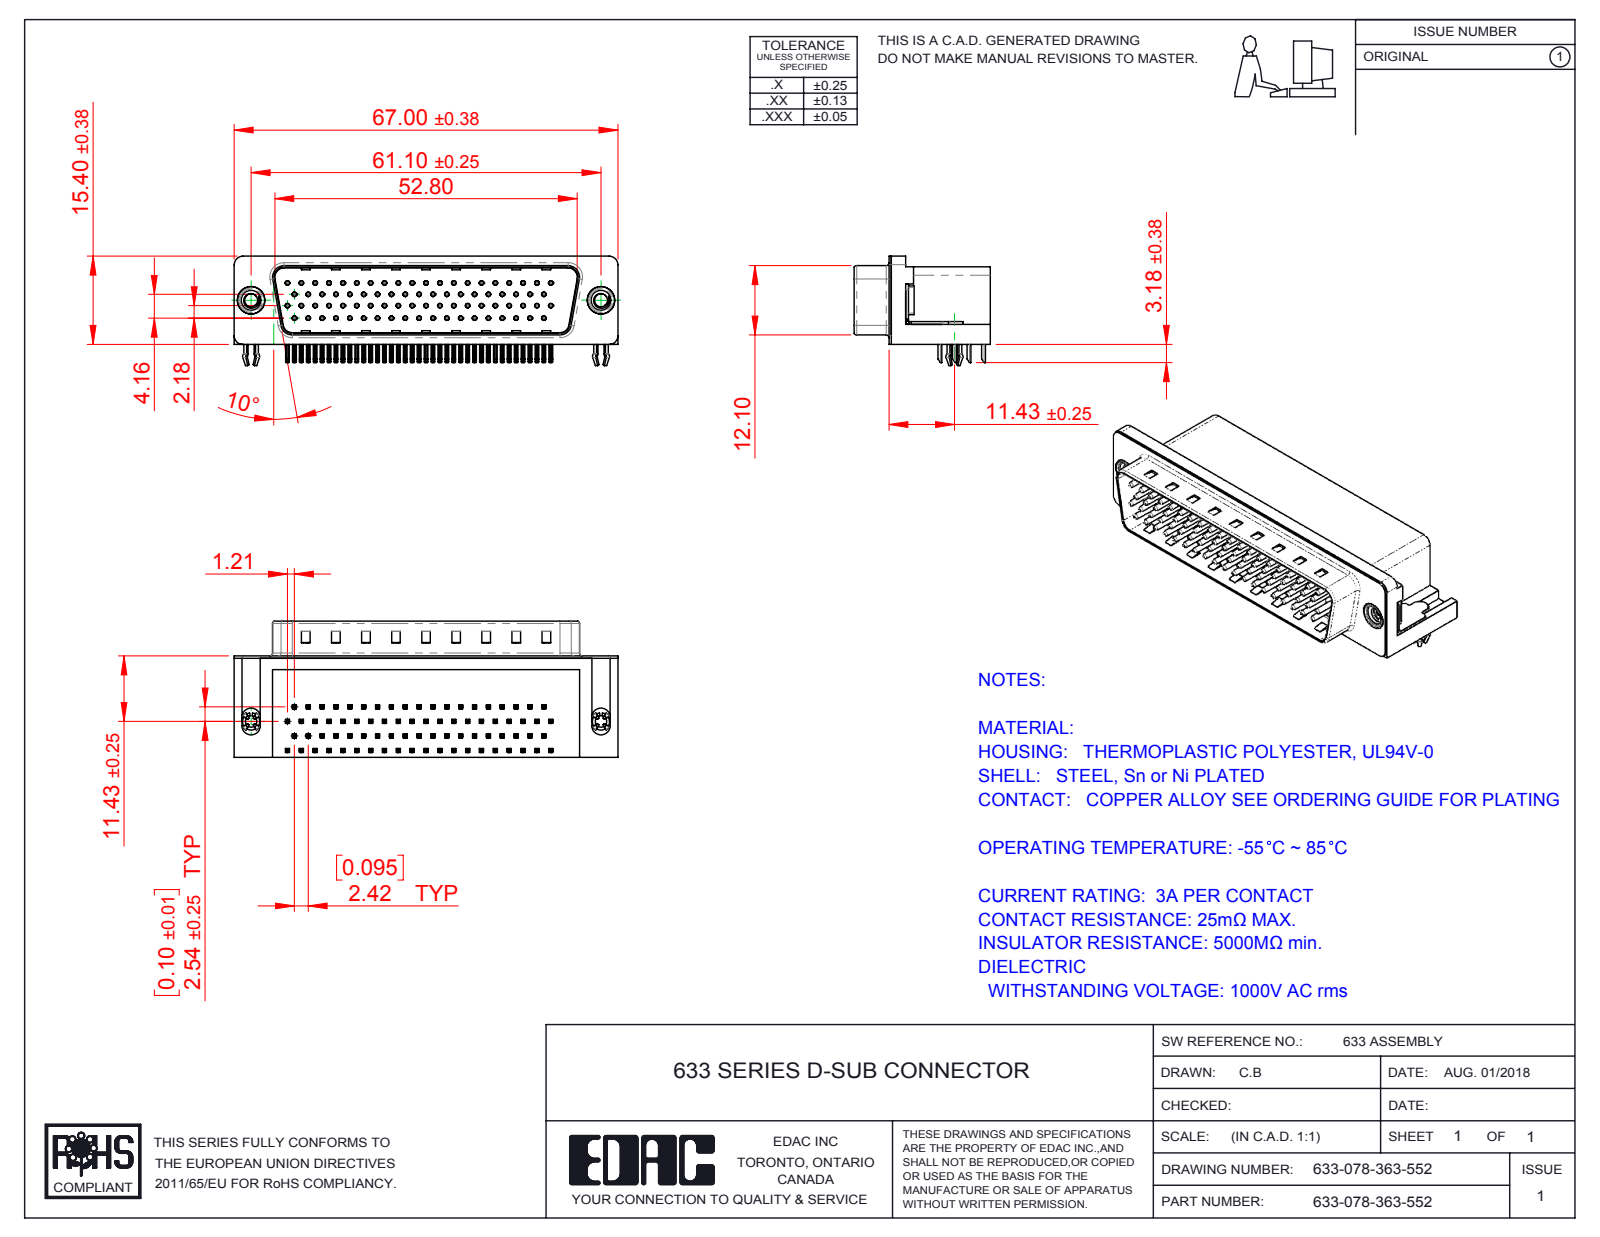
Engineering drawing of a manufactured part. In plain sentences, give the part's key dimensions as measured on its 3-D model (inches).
The part is named "633 Contact Bottom_78 Contact; 633-078-363-552; 633 4 Prong Board Lock_78 Contact; 633 4-40 Threaded Rivet (+5 more)". Its 3-D file was written by "SolidWorks 2016 (CONFIG_CONTROL_DESIGN)". It is 84 solids with 6396 faces: 4023 planar, 1784 cylindrical and 589 other. Overall it measures 2.638 by 0.937 by 0.752 inches. Its volume is 0.892 cubic inches and its surface area 25.47 square inches. Round holes: 78 of diameter 0.014, 78 of diameter 0.031, 2 of diameter 0.079, 2 of diameter 0.089, 2 of diameter 0.157, 2 of diameter 0.189, 2 of diameter 0.197. Round bosses or shafts: 78 of diameter 0.03, 2 of diameter 0.193, 2 of diameter 0.187, 2 of diameter 0.154, 2 of diameter 0.118. Partial cylindrical surfaces (rounded edges, fillets, slot ends): 324 of radius 0.01, 156 of radius 0.005, 16 of radius 0.039, 9 of radius 0.02, 8 of radius 0.063, 6 of radius 0.059, 4 of radius 0.018, 4 of radius 0.035. The main face-to-face distances are 0.016, 0.52, 0.681, 0.461, 0.526, 0.081, 0.541, 0.065, 0.073, 0.469. The hole center spacings are 0.095, 0.191, 0.286, 0.381, 0.246, 0.281, 0.476, 0.339.
